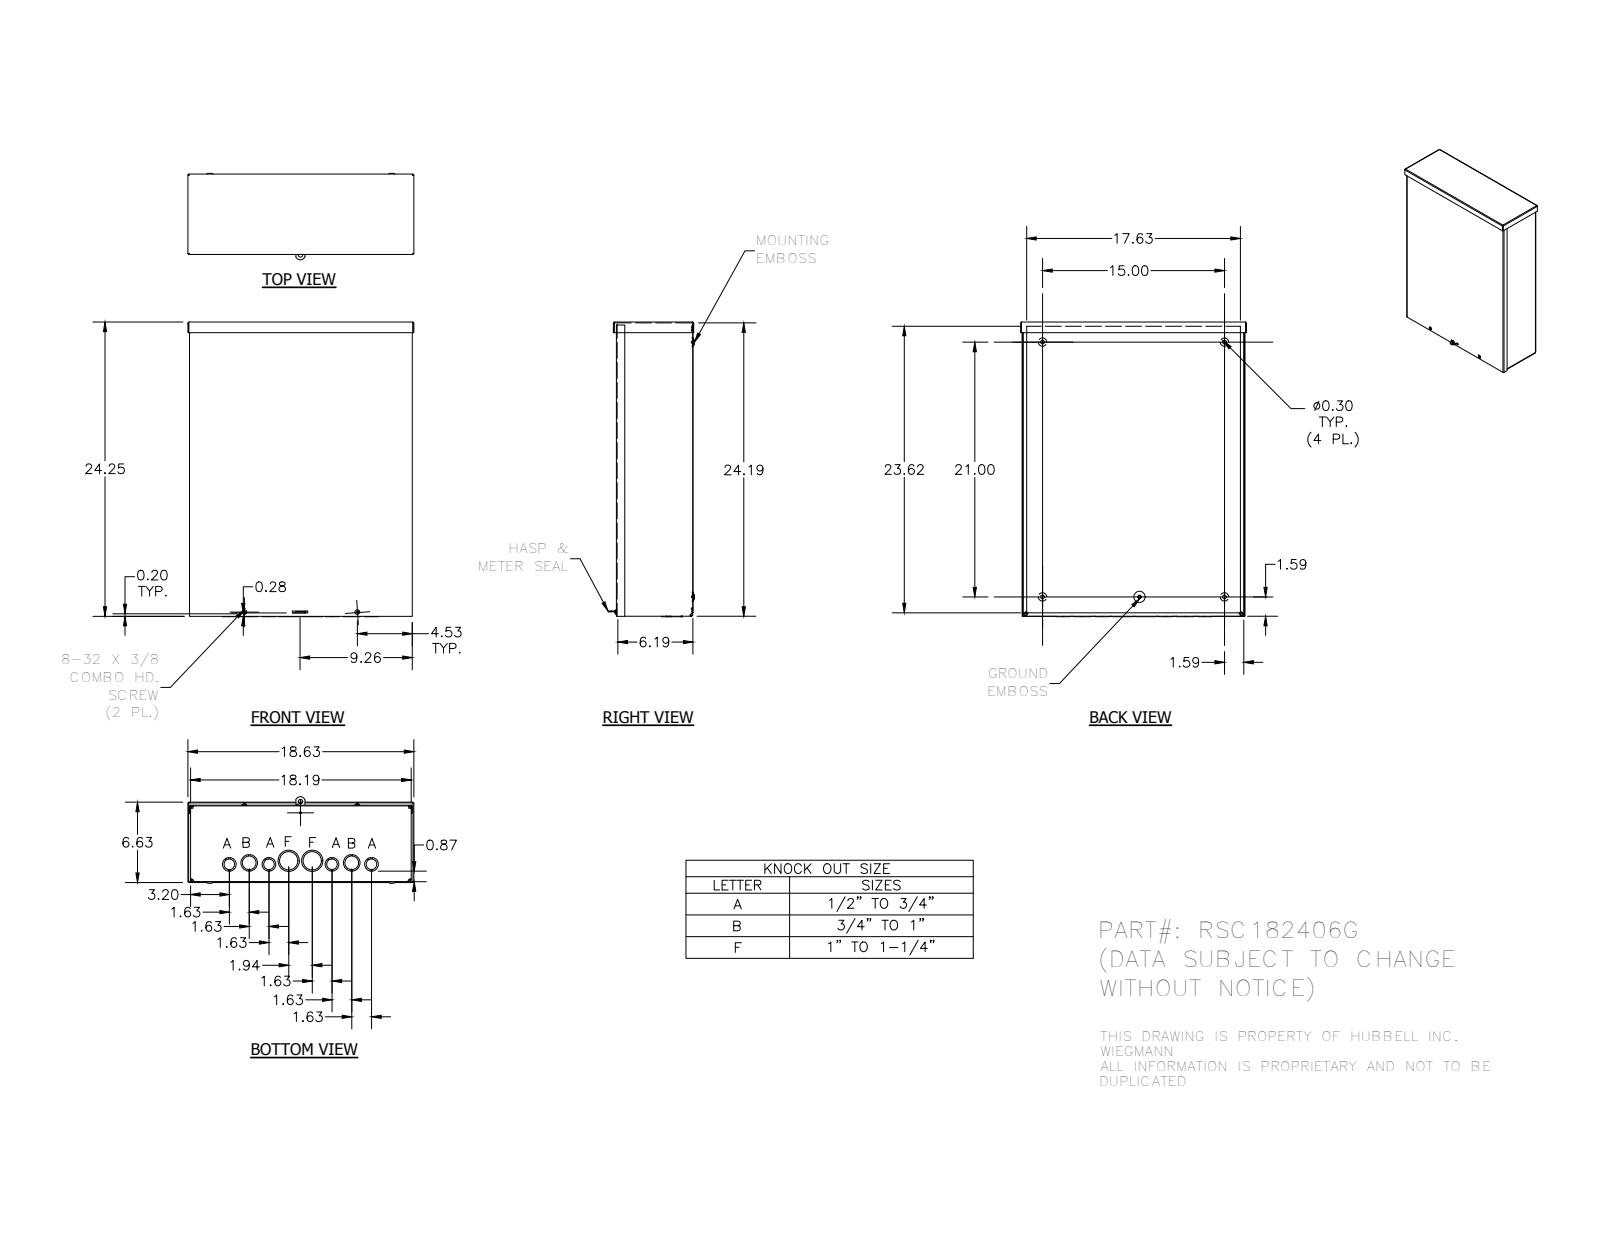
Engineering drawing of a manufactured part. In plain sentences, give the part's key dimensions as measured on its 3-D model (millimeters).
The part is named "RSC182406G_WRAP; RSC1824G_LID; RSC1806G_CAP; 3183 (+4 more)". Its 3-D file was written by "Autodesk Inventor 2014 (AUTOMOTIVE_DESIGN)". It is 7 solids with 619 faces: 304 planar, 171 cylindrical and 144 other. Overall it measures 616.73 by 473.07 by 180.97 millimeters. Its volume is 1 723 000 cubic millimeters and its surface area 2 204 000 square millimeters. Round holes: 6 of diameter 28.57, 4 of diameter 7.62, 4 of diameter 7.95, 4 of diameter 22.22, 2 of diameter 3.17, 2 of diameter 3.76, 2 of diameter 34.92, 2 of diameter 38.1, 2 of diameter 44.45, 1 of diameter 3.96, 1 of diameter 4.19, 1 of diameter 9.52. Round bosses or shafts: 2 of diameter 9.75, 2 of diameter 4.17, 1 of diameter 5.8. Partial cylindrical surfaces (rounded edges, fillets, slot ends): 15 of radius 0.25, 8 of radius 0.79, 8 of radius 2.37, 8 of radius 3.17, 8 of radius 4.75, 6 of radius 0.79, 5 of radius 0.63, 4 of radius 1.4. The main face-to-face distances are 1.58, 158.73, 157.15, 1.59, 160.32, 158.74, 1.57, 460.39, 612.79, 3.15. The hole center spacings are 41.52, 214.88, 42.07, 82.8, 82.91, 90.99, 124.42, 126.18.
